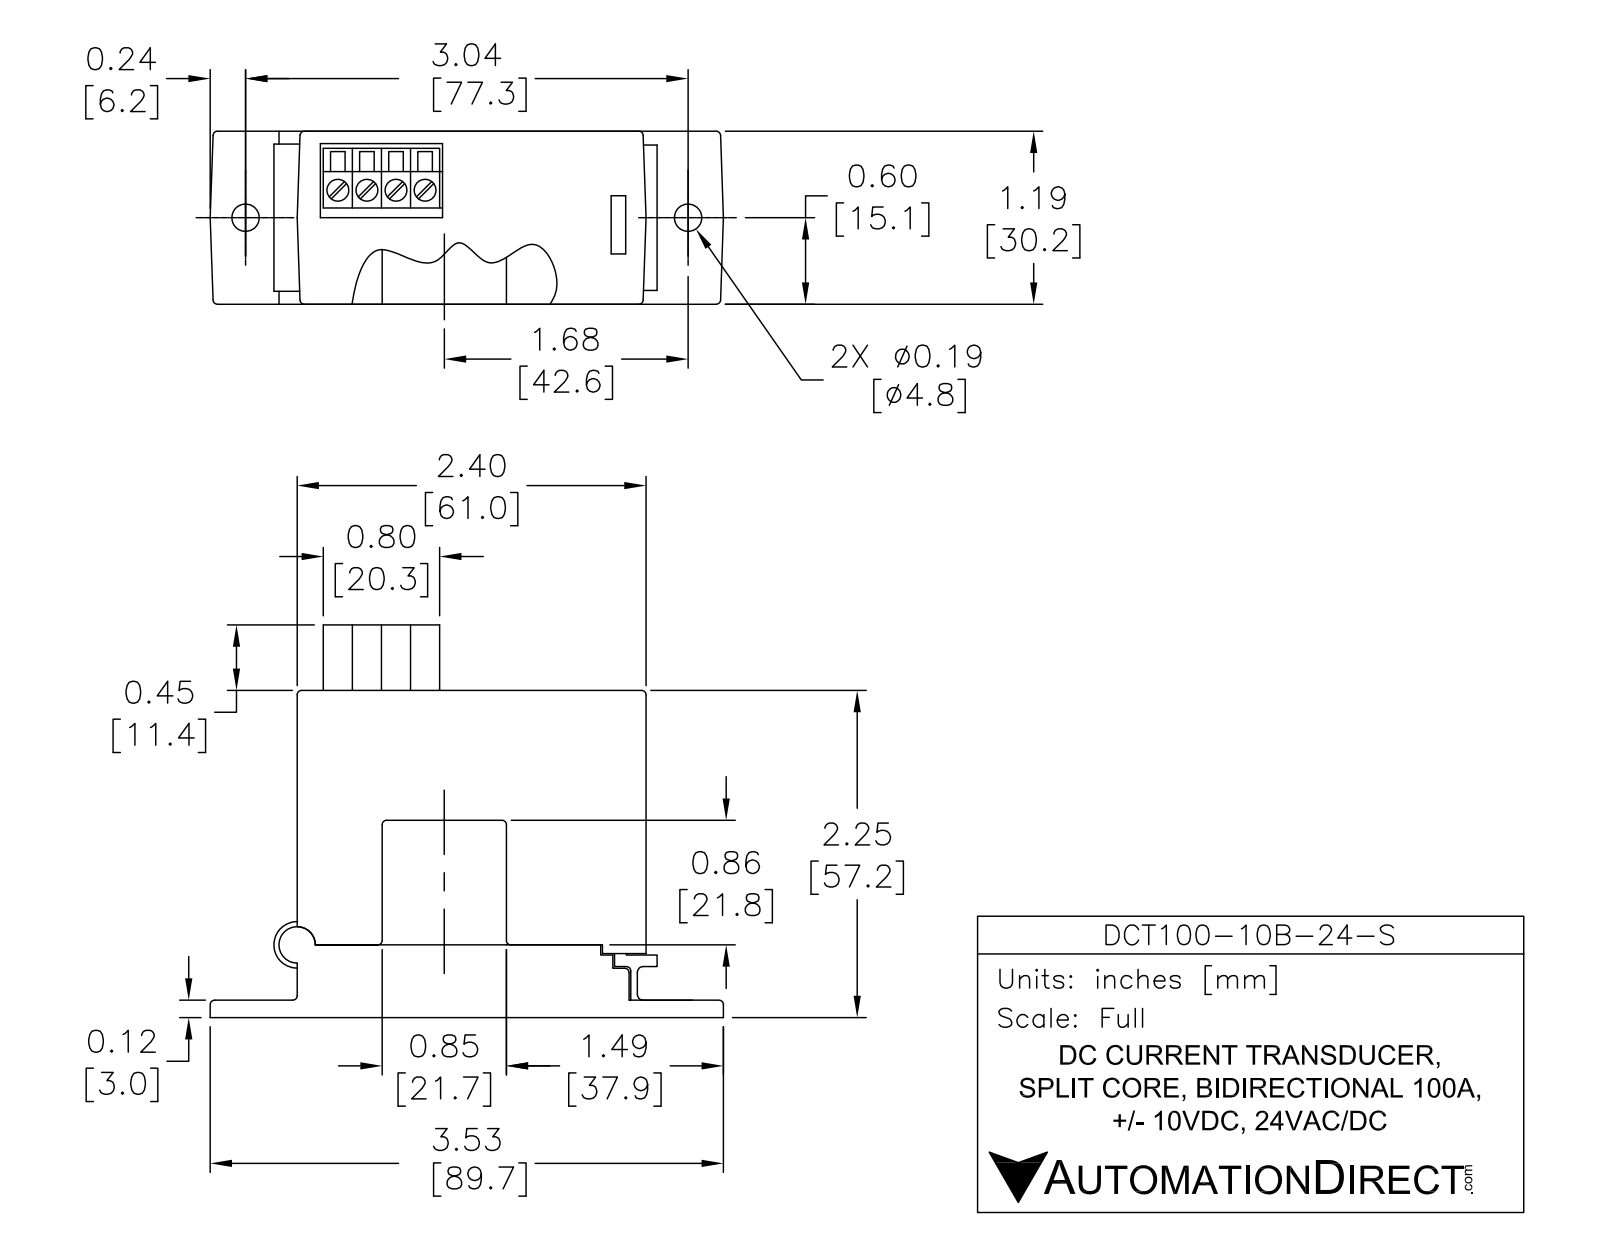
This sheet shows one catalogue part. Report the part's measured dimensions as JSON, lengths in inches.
{"part_name": "DCT100-10B-24-S", "step_written_by": "SolidWorks 2017 (AUTOMOTIVE_DESIGN)", "units": "inches", "bodies": {"solids": 4, "faces": 158, "planar": 100, "cylindrical": 50, "other": 8}, "overall_size": [3.531, 2.7, 1.189], "volume_in3": 5.725, "surface_area_in2": 35.03, "round_holes": [[0.157, 4], [0.188, 2], [0.26, 1]], "round_bosses_or_shafts": [[0.25, 1]], "partial_cylinders_radius": [[0.03, 22], [0.16, 1], [0.17, 1]], "face_to_face_distances": [1.189, 2.252, 0.5, 1.752, 2.399, 0.505, 1.747, 0.118, 0.382, 0.387], "hole_center_spacings": [0.197, 0.398, 0.201, 0.596, 0.632, 0.822, 1.019, 1.213]}
